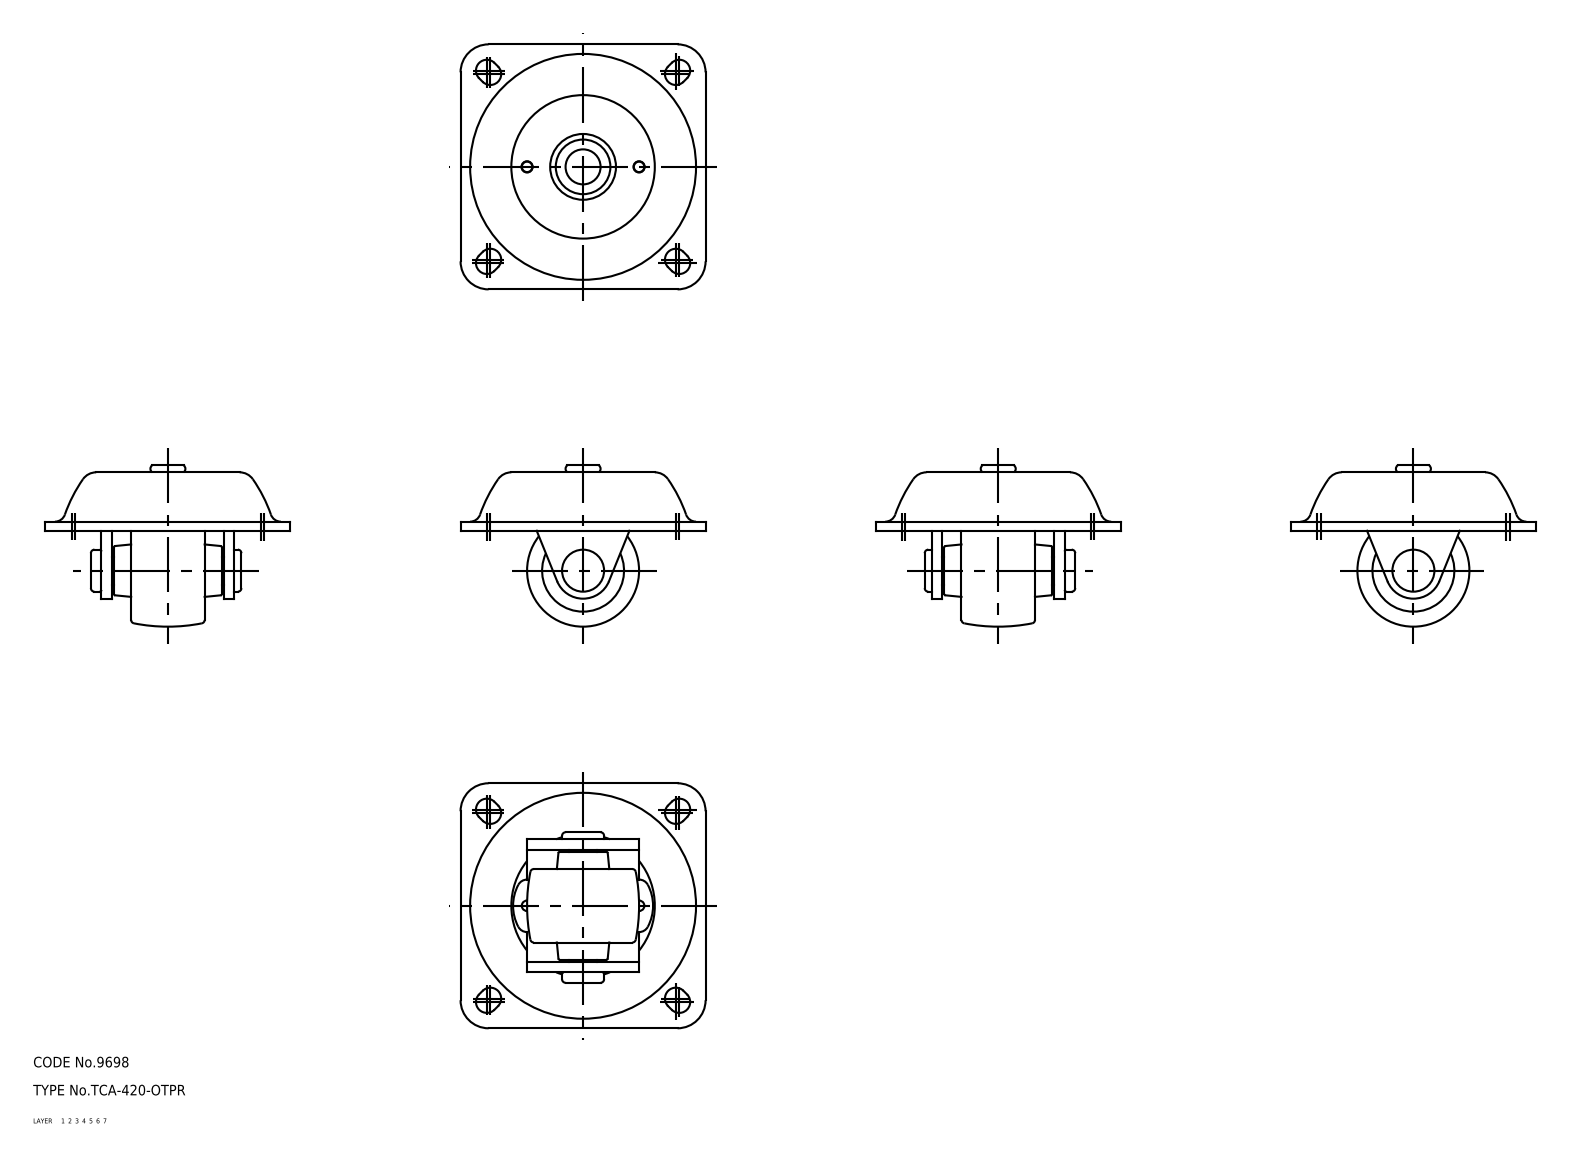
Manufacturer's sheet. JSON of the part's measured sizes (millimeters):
{"part_name": "wheel; mounting plate; main shaft; axle (+1 more)", "step_written_by": "CADfix (AUTOMOTIVE_DESIGN)", "units": "millimeters", "bodies": {"solids": 5, "faces": 193, "planar": 0, "cylindrical": 0, "other": 193}, "overall_size": [70, 70, 46.1], "volume_mm3": 41242, "surface_area_mm2": 25988}
